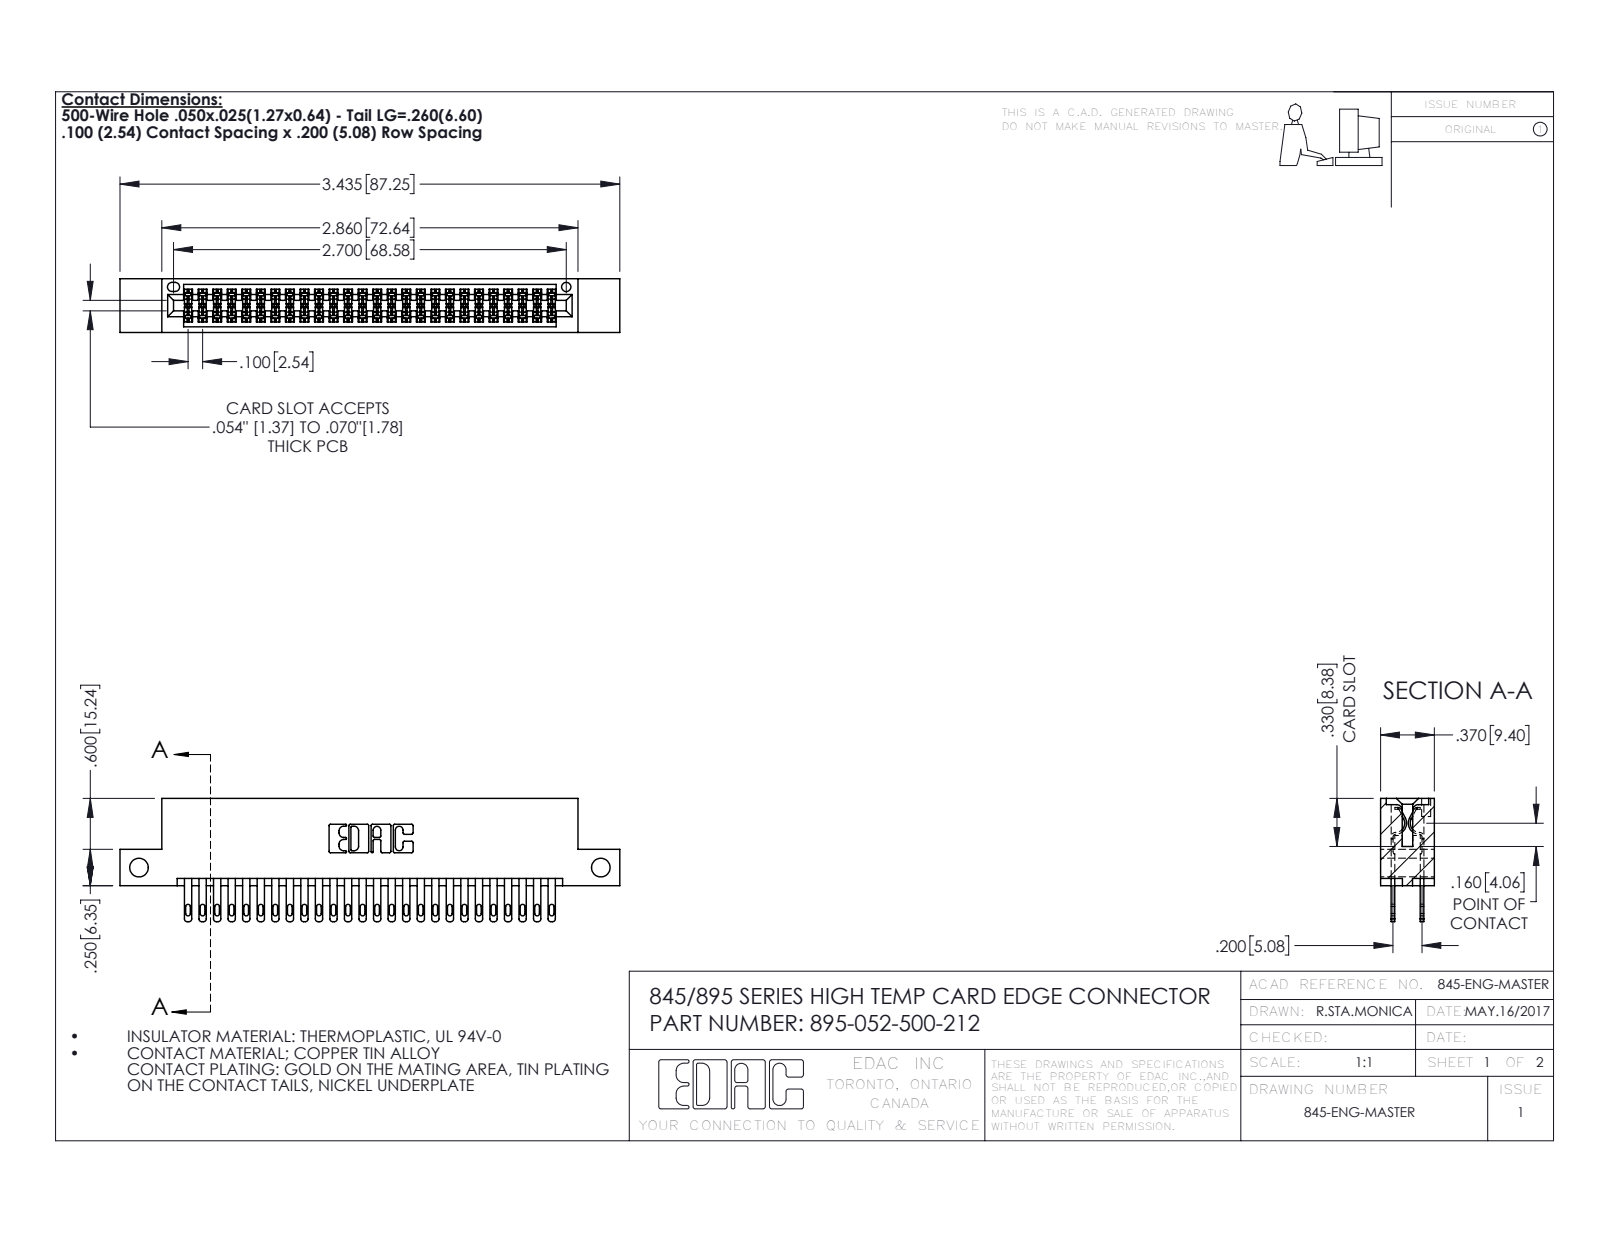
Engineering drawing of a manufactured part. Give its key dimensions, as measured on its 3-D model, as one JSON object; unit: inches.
{"part_name": "345-292-001_345-293-100; 845 Part_Flush Mounting Lugs - Side Mount; 895-052-500-212", "step_written_by": "SolidWorks 2020 (CONFIG_CONTROL_DESIGN)", "units": "inches", "bodies": {"solids": 53, "faces": 2518, "planar": 1484, "cylindrical": 1034, "other": 0}, "overall_size": [3.435, 0.847, 0.37], "volume_in3": 0.513, "surface_area_in2": 19.37, "round_holes": [[0.128, 2], [0.064, 1]], "partial_cylinders_radius": [[0.006, 78], [0.016, 52], [0.02, 52], [0.01, 22], [0.007, 6], [0.031, 6], [0.026, 3], [0.014, 2]], "face_to_face_distances": [0.298, 0.072, 0.2, 0.098, 0.272, 0.025, 0.37, 0.225, 0.175, 0.149], "hole_center_spacings": [3.175]}
